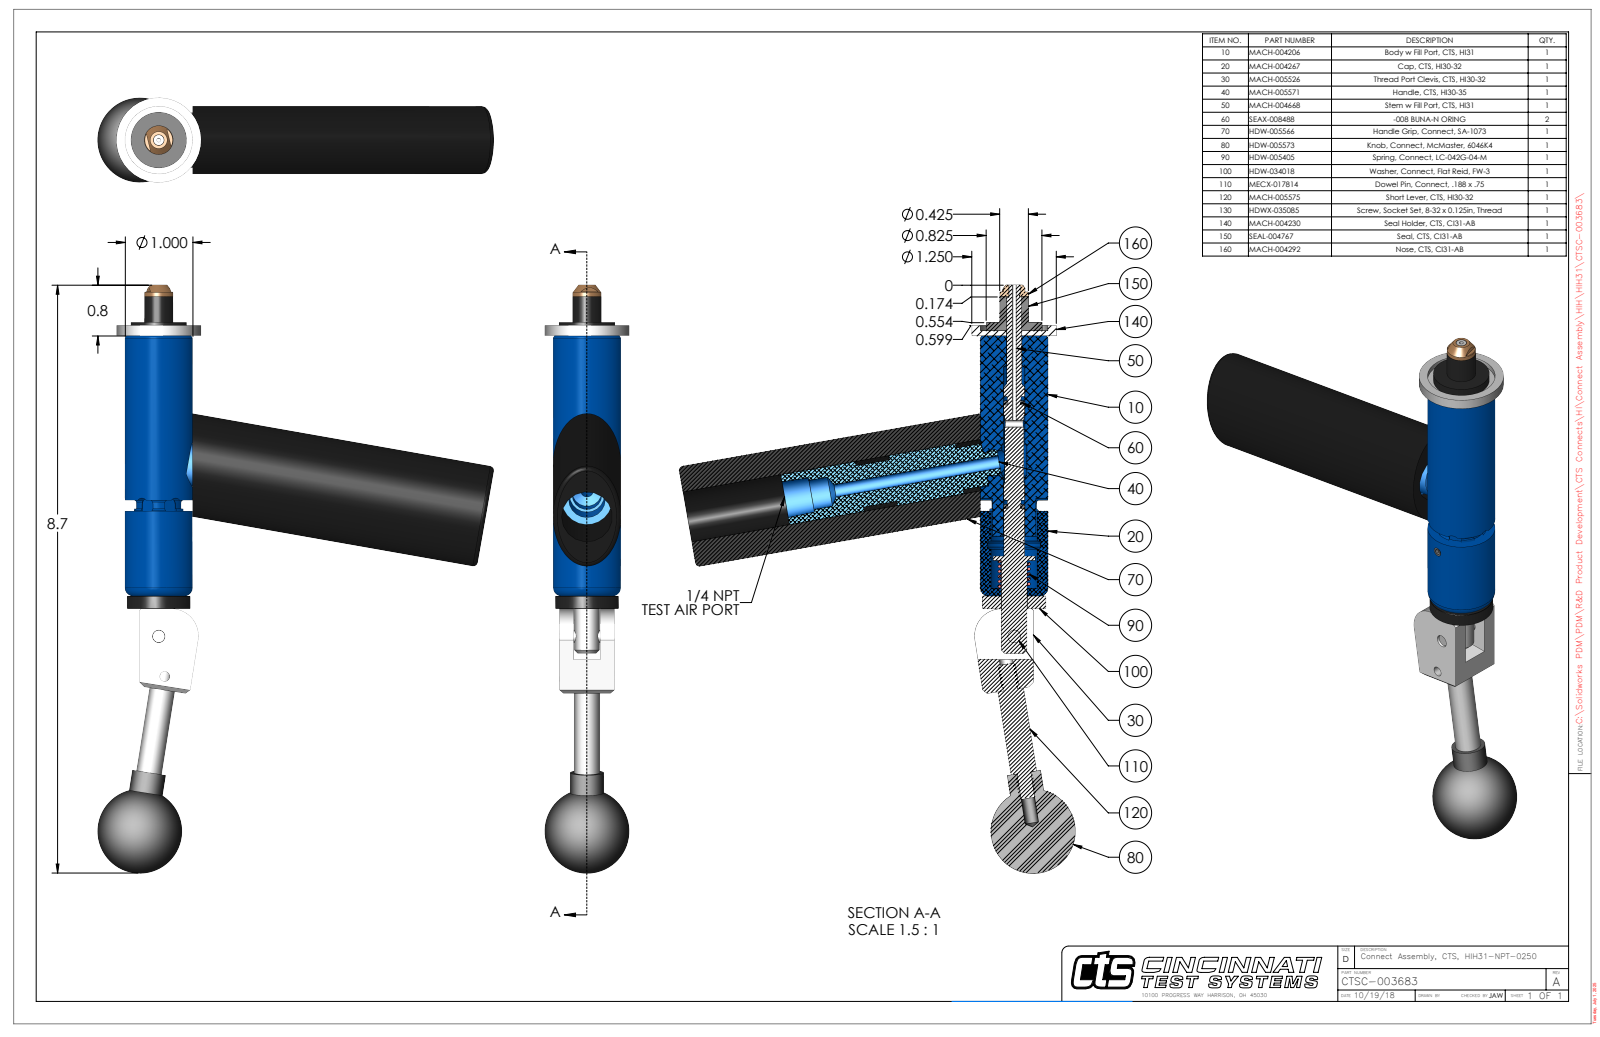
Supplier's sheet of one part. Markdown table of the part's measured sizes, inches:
| quantity | value |
| --- | --- |
| part name | CTSC-003683 |
| STEP written by | SolidWorks 2023 (AUTOMOTIVE_DESIGN) |
| units | inches |
| bodies | 10 solids, 326 faces (124 planar, 132 cylindrical, 70 other) |
| overall size | 8.692 × 5.856 × 1.25 |
| volume | 9.408 in³ |
| surface area | 78.29 in² |
| round holes (diameter × count) | 0.201 × 2, 0.063 × 1, 0.109 × 1, 0.136 × 1, 0.15 × 1, 0.159 × 1, 0.187 × 1, 0.189 × 1, 0.218 × 1, 0.228 × 1, 0.229 × 1, 0.385 × 1 |
| round bosses / shafts (diameter × count) | 1.25 × 1, 1 × 1, 0.936 × 1, 0.825 × 1, 0.75 × 1, 0.62 × 1, 0.5 × 1, 0.427 × 1 |
| partial cylindrical surfaces (radius × count) | 0.093 × 6, 0.029 × 2, 0.066 × 1, 0.325 × 1, 0.375 × 1, 0.4 × 1, 0.452 × 1 |
| main face-to-face distances | 0.072, 0.21, 0.602, 3.916, 3.844, 0.812, 4.103, 4.031, 0.187, 0.391 |
| hole center spacings | 0.599, 1.658, 2.252 |
